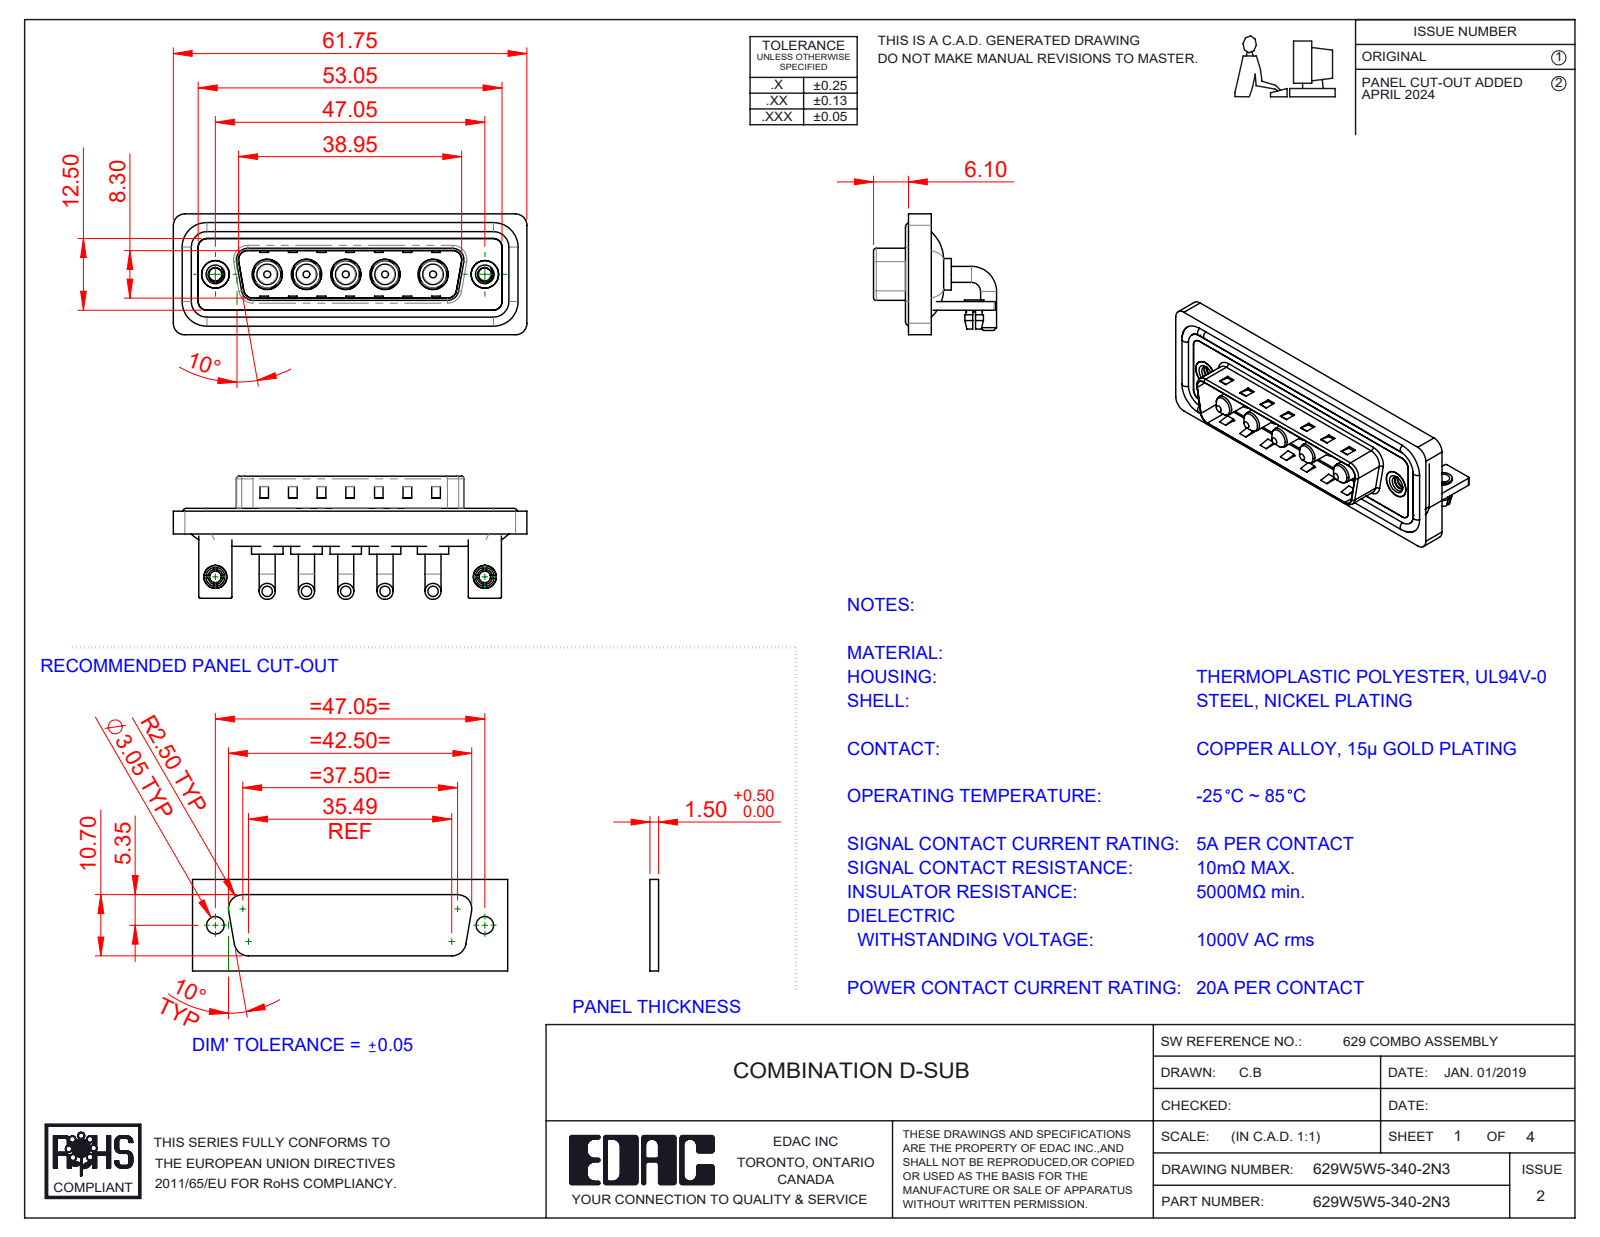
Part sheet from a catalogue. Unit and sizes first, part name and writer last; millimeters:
Units: millimetres
Overall size (bounding box): 61.75 × 21.5 × 21.1
Round holes (diameter × count): ⌀4.85 ×5, ⌀5.3 ×5, ⌀2 ×2, ⌀2.26 ×2, ⌀2.5 ×2, ⌀3.2 ×2, ⌀4 ×2, ⌀4.8 ×2, ⌀5 ×2
Round bosses / shafts (diameter × count): ⌀2.8 ×10, ⌀5.5 ×5, ⌀5.2 ×5, ⌀4.75 ×5, ⌀3.75 ×5, ⌀3.6 ×5, ⌀1.6 ×4, ⌀4.9 ×2
Partial cylindrical surfaces — rounded edges, fillets, slot ends (radius × count): R2 ×19, R1.5 ×18, R0.25 ×16, R0.5 ×9, R1.6 ×8, R2.1 ×5, R0.6 ×4, R0.65 ×4
Main face-to-face distances: 0.4, 1.5, 2.9, 0.8, 2.1, 1.1, 3.7, 4.5, 4.1, 1.2
Hole centre spacings: 6.86, 13.73, 47.05, 6.85, 6.87, 8.37, 8.38, 9.04
Volume: 8 116 mm³ · Surface area: 13 069 mm²
Bodies: 21 solids, 830 faces (327 planar, 343 cylindrical, 160 other)
Part name (STEP PRODUCT): 629Combo Board Lock; 629Combo Stabilizer Bracket; Power Pin_20A RA; 629Combo Shell Front_25 Contacts (+5 more)
STEP written by: SolidWorks 2023 (CONFIG_CONTROL_DESIGN)
